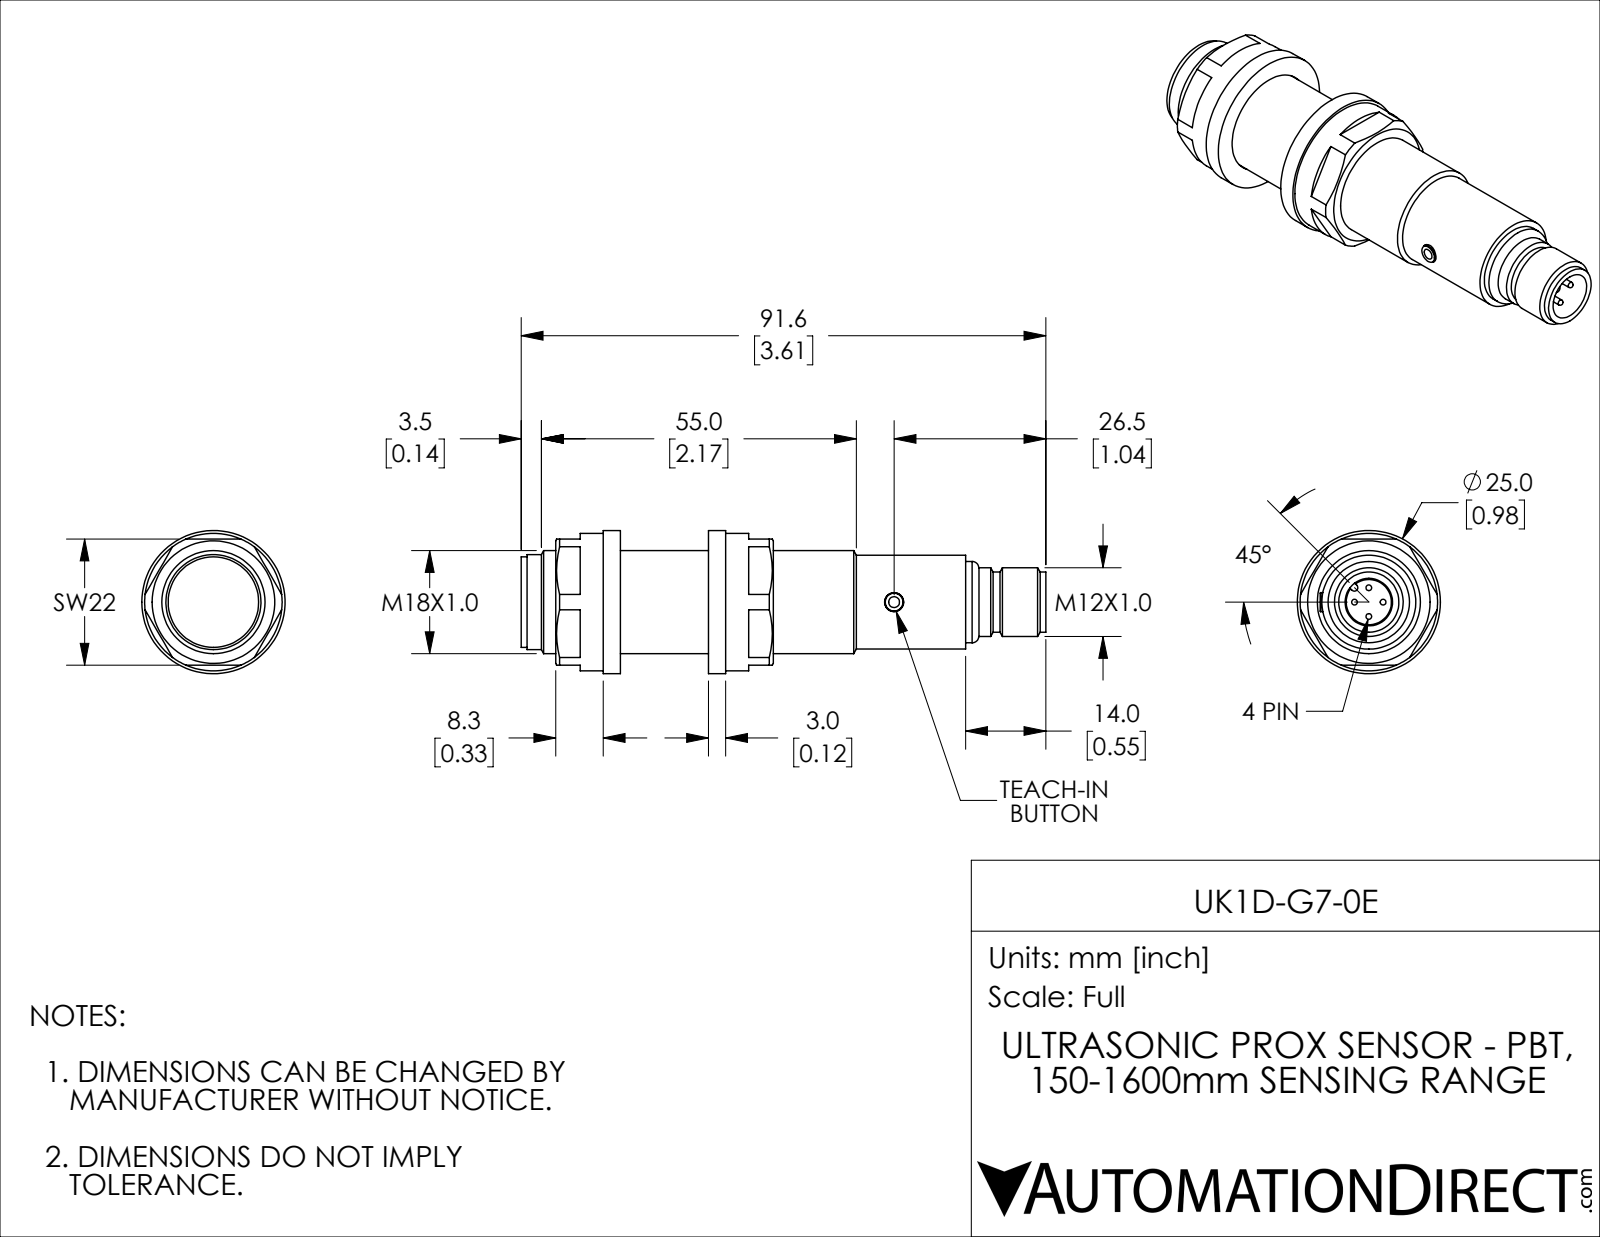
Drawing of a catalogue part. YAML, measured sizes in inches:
part_name: "UK1D-G7-0E"
step_written_by: "SolidWorks 2018 (AUTOMOTIVE_DESIGN)"
units: inches
bodies: {solids: 6, faces: 123, planar: 43, cylindrical: 49, other: 31}
overall_size: [3.606, 0.984, 0.984]
volume: 1.477
surface_area: 16.01
round_holes:
  - {diameter: 0.13, count: 1}
  - {diameter: 0.327, count: 1}
  - {diameter: 0.709, count: 1}
  - {diameter: 0.717, count: 1}
round_bosses_or_shafts:
  - {diameter: 0.039, count: 4}
  - {diameter: 0.984, count: 1}
  - {diameter: 0.945, count: 1}
  - {diameter: 0.654, count: 1}
  - {diameter: 0.646, count: 1}
  - {diameter: 0.622, count: 1}
  - {diameter: 0.559, count: 1}
  - {diameter: 0.472, count: 1}
partial_cylinders:
  - {radius: 0.024, count: 1}
face_to_face_distances: [0.118, 0.724, 0.843, 0.606, 0.866, 0.327, 0.445, 1.051, 1.169, 0.563]
